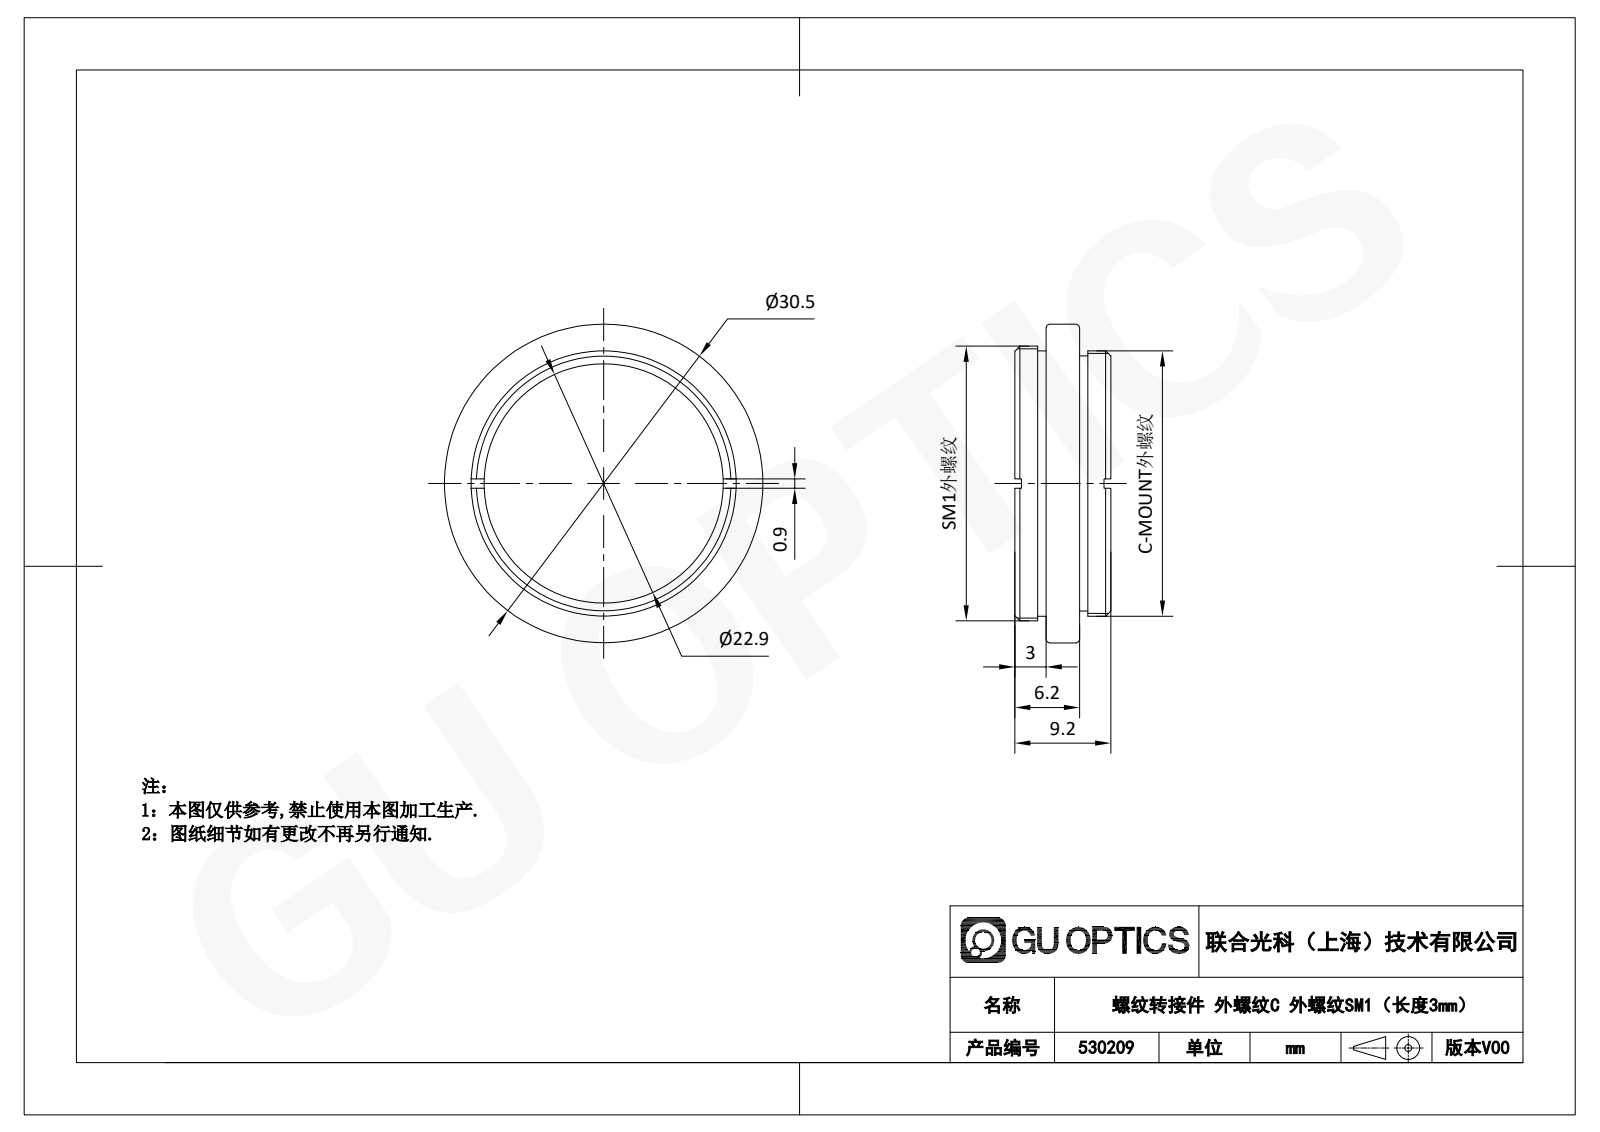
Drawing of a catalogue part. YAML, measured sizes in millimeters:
part_name: "530209"
step_written_by: "SolidWorks 2020 (CONFIG_CONTROL_DESIGN)"
units: millimeters
bodies: {solids: 1, faces: 36, planar: 20, cylindrical: 6, other: 10}
overall_size: [30.5, 30.5, 9.2]
volume: 1607
surface_area: 2150
round_holes:
  - {diameter: 22.9, count: 1}
round_bosses_or_shafts:
  - {diameter: 30.5, count: 1}
  - {diameter: 26.29, count: 1}
  - {diameter: 25.4, count: 1}
  - {diameter: 24.4, count: 1}
face_to_face_distances: [3.2, 3, 6.2, 0.8, 4, 7, 2.2, 4.8, 9.2, 0.65]
